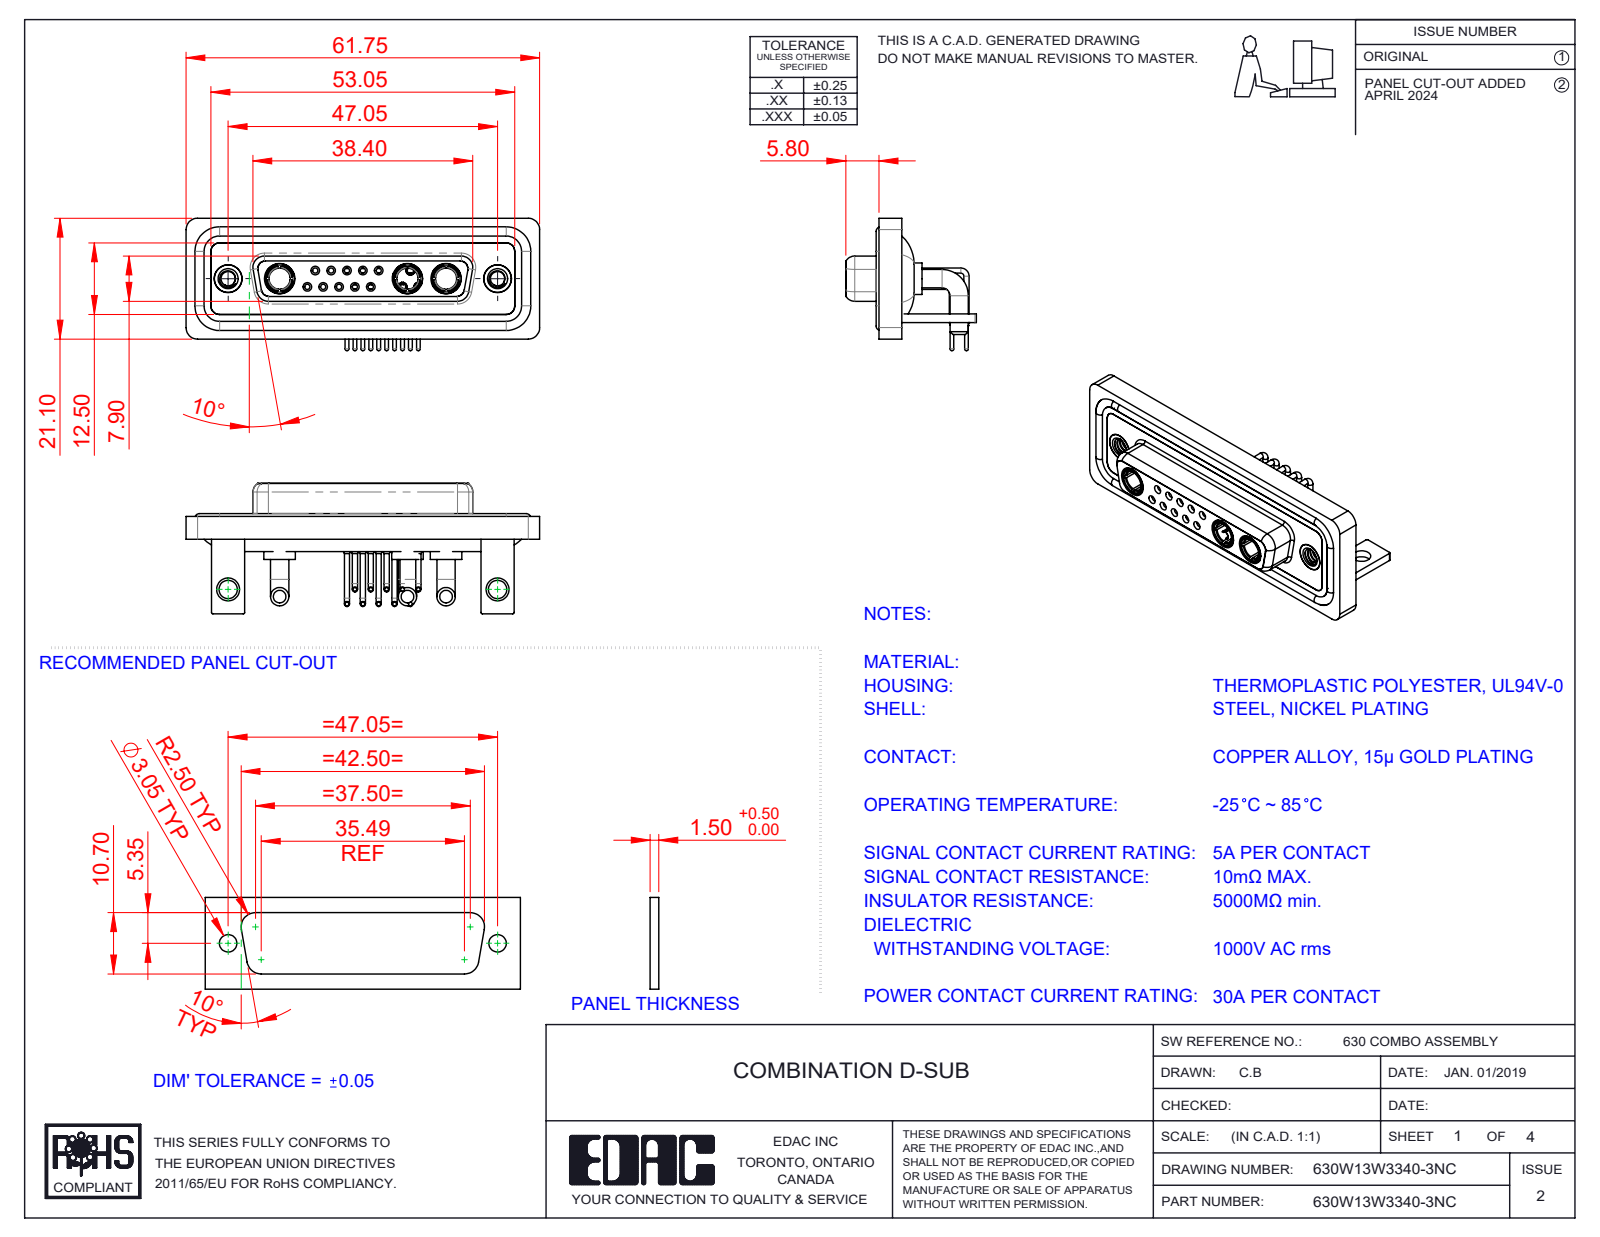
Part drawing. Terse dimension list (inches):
name: 630Combo Contact Row 2_50 Contacts; 630Combo Shell Rear_25 Contacts; 630Combo Stabilizer Bracket_50 Contacts; 630W13W3340-3NC (+6 more)
written by: SolidWorks 2023 (CONFIG_CONTROL_DESIGN)
unit: in
bodies: 25 solids, 1192 faces (362 planar, 515 cylindrical, 315 other)
size: 2.431 × 0.91 × 0.898
volume: 0.544 in³; area: 23.39 in²
holes: 10× ⌀0.035, 10× ⌀0.043, 10× ⌀0.059, 10× ⌀0.079, 5× ⌀0.063, 5× ⌀0.067, 5× ⌀0.191, 3× ⌀0.146, 3× ⌀0.209, 2× ⌀0.098, 2× ⌀0.126, 2× ⌀0.157
bosses: 15× ⌀0.035, 12× ⌀0.063, 10× ⌀0.026, 6× ⌀0.126, 5× ⌀0.079, 5× ⌀0.059, 3× ⌀0.217, 3× ⌀0.205
rounds: 19× R0.079, 18× R0.059, 16× R0.01, 8× R0.053, 8× R0.063, 5× R0.02, 4× R0.024, 4× R0.026
face distances: 0.016, 0.071, 0.114, 0.146, 0.059, 0.161, 0.043, 0.055, 0.063, 0.122
hole spacings: 0.124, 0.109, 0.218, 0.198, 0.327, 0.198, 0.295, 0.436
